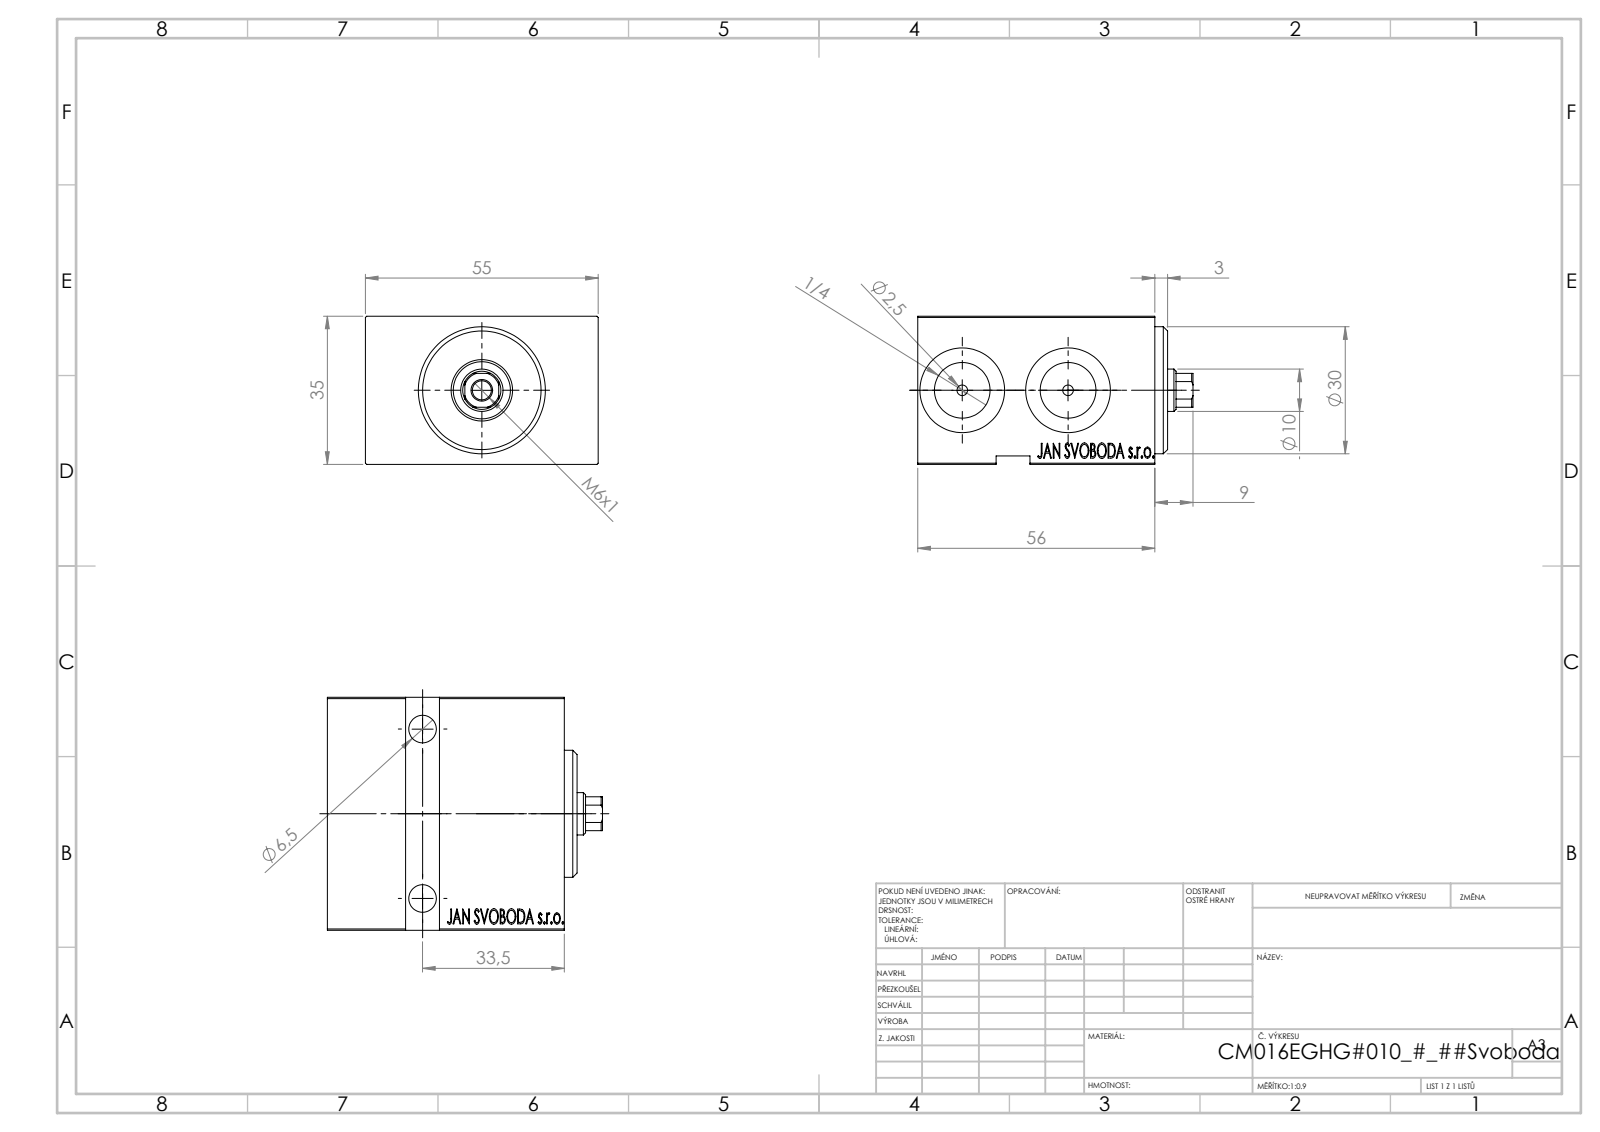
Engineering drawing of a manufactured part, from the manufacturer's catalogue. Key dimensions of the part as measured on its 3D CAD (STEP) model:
Part name (STEP PRODUCT): V450CM_VC_B; V450CM_E_Body; V450CM_E_VCP
STEP written by: SolidWorks 2019 (CONFIG_CONTROL_DESIGN)
Units: millimetres
Bodies: 3 solids, 849 faces (409 planar, 46 cylindrical, 394 other)
Overall size (bounding box): 65 × 55 × 35
Volume: 102 280 mm³ · Surface area: 25 663 mm²
Round holes (diameter × count): ⌀2.5 ×2, ⌀6.5 ×2, ⌀10.5 ×2, ⌀13.16 ×2, ⌀20 ×2, ⌀4.5 ×1, ⌀10 ×1, ⌀13.5 ×1, ⌀14.5 ×1, ⌀16 ×1, ⌀25 ×1
Round bosses / shafts (diameter × count): ⌀30 ×1, ⌀18 ×1
Partial cylindrical surfaces — rounded edges, fillets, slot ends (radius × count): R4.5 ×1
Main face-to-face distances: 35, 56, 55, 5, 51, 8, 3, 59, 46, 54
Hole centre spacings: 25, 40
